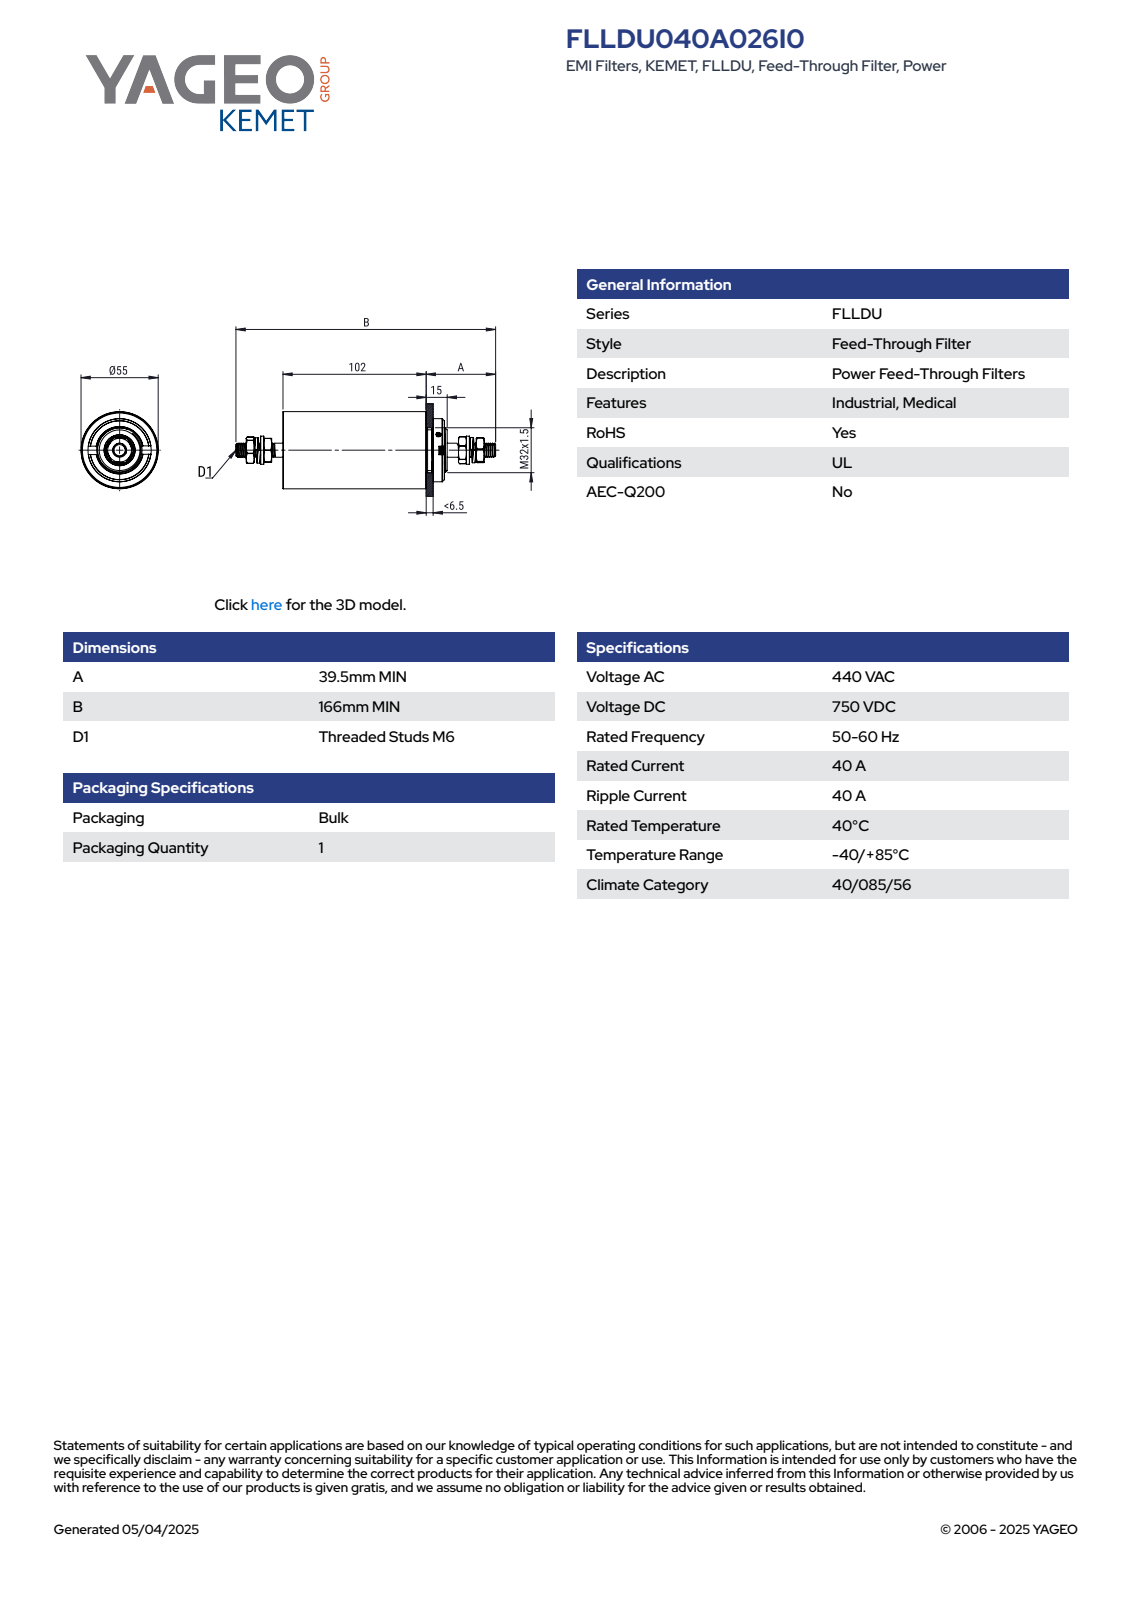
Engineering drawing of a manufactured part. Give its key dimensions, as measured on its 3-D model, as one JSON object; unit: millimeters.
{"part_name": "HEX NUT M6x1 THIN_90695A038; DIC0013; WASHER M6 Ø12_93475A250; GEH0061 (+6 more)", "step_written_by": "SolidWorks 2021 (AUTOMOTIVE_DESIGN)", "units": "millimeters", "bodies": {"solids": 14, "faces": 466, "planar": 63, "cylindrical": 226, "other": 177}, "overall_size": [166, 55, 55], "volume_mm3": 47732, "surface_area_mm2": 58330, "round_holes": [[6.4, 1], [22, 1], [30.4, 1], [53, 1]], "round_bosses_or_shafts": [[55, 1], [54, 1], [45, 1], [32, 1], [29, 1], [22.1, 1], [12, 1], [6, 1]], "partial_cylinders_radius": [[0.15, 12], [0.2, 12]], "face_to_face_distances": [4, 102, 98, 10, 5, 103, 107, 8, 111, 13]}
